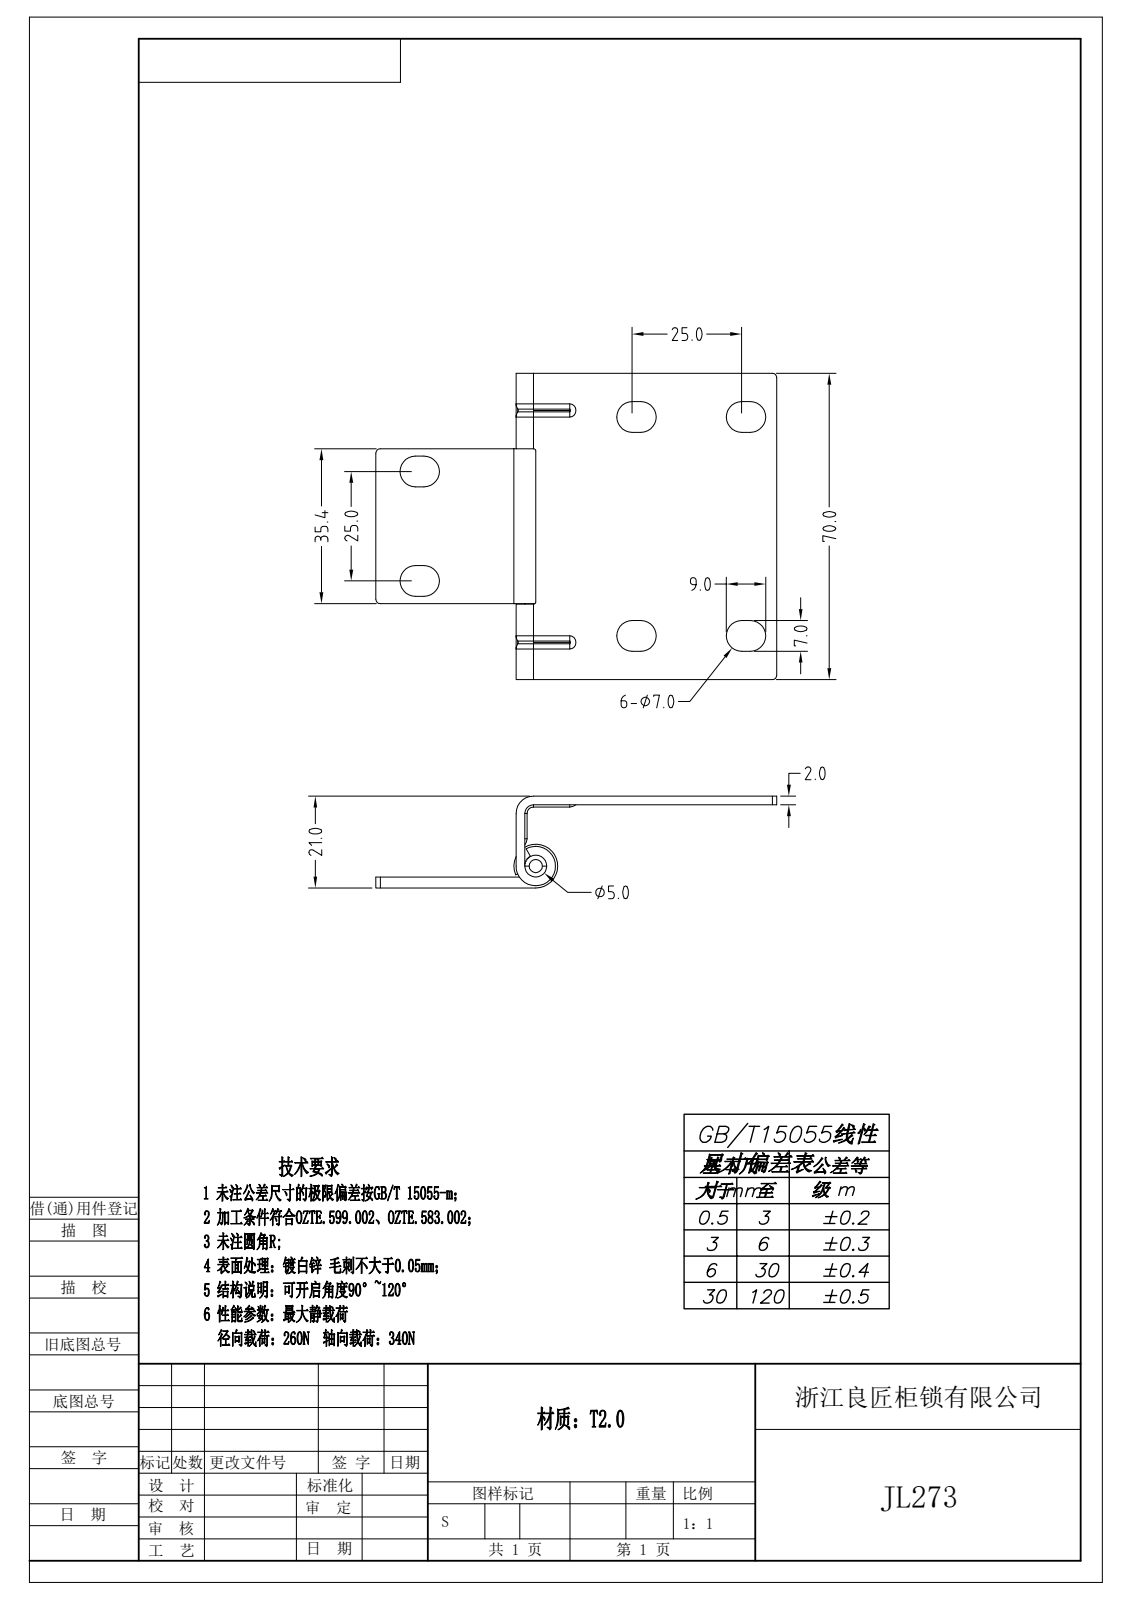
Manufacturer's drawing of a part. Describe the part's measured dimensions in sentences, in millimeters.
Its 3-D file was written by "Rhino 8.5 (CONFIG_CONTROL_DESIGN)". It is 2 solids with 100 faces: 36 planar, 42 cylindrical and 22 other. Overall it measures 91.5 by 70 by 21 millimeters. Its volume is 5 999 cubic millimeters and its surface area 16 157 square millimeters. Round holes: 1 of diameter 5. Round bosses or shafts: 1 of diameter 10, 1 of diameter 9. Partial cylindrical surfaces (rounded edges, fillets, slot ends): 12 of radius 3.5, 6 of radius 0.5, 4 of radius 1, 1 of radius 2, 1 of radius 4. The main face-to-face distances are 2, 19, 16.5, 18.5, 2.5, 21, 17.3, 52.7, 70, 17.25.
